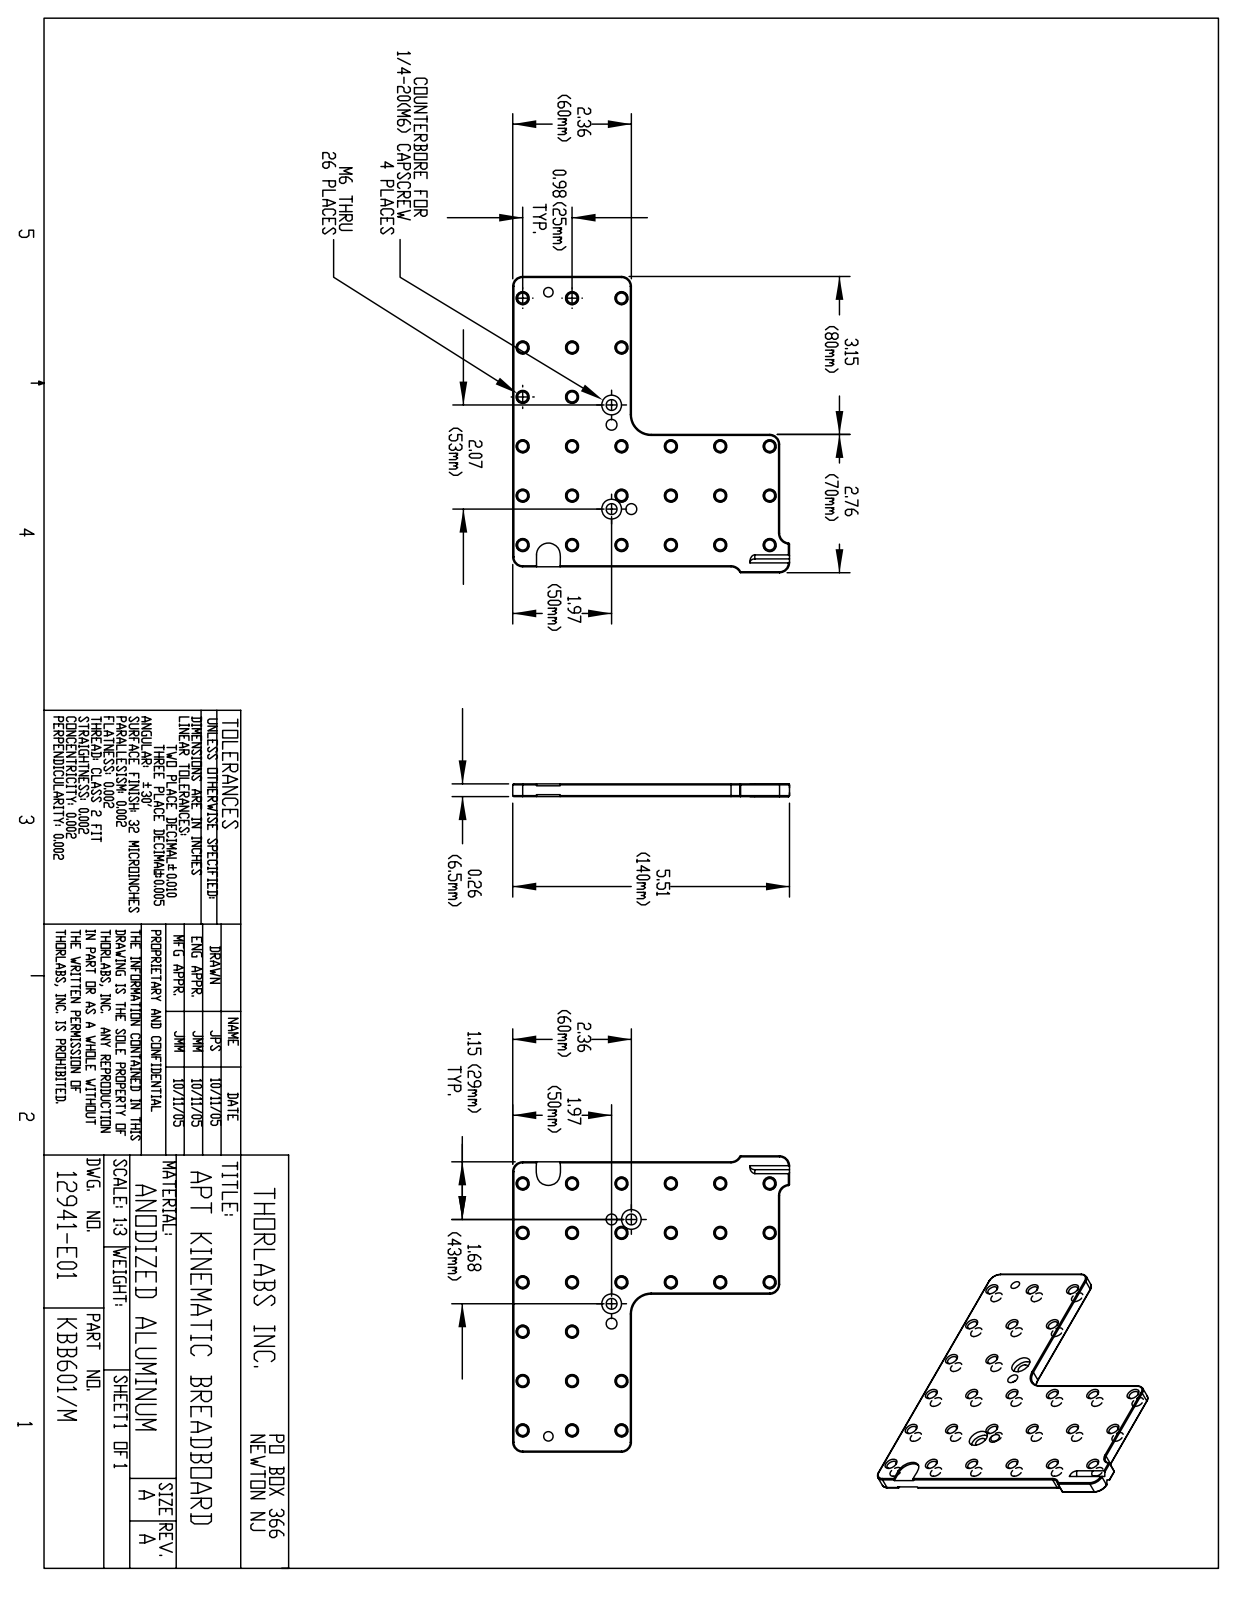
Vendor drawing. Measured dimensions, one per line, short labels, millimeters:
name: 12941-E0W
written by: SolidWorks 2007 (AUTOMOTIVE_DESIGN)
unit: mm
bodies: 0 solids, 253 faces (24 planar, 101 cylindrical, 128 other)
size: 150 × 140 × 6.5
holes: 26× ⌀5, 4× ⌀5.5, 4× ⌀10
rounds: 18× R0.5, 7× R5, 2× R2.5, 1× R6, 1× R10
face distances: 6.5, 2.7, 1, 60, 67, 80, 147, 5.5, 75, 135
hole spacings: 55.9, 25, 35.4, 79.1, 50, 90.1, 103.1, 125
